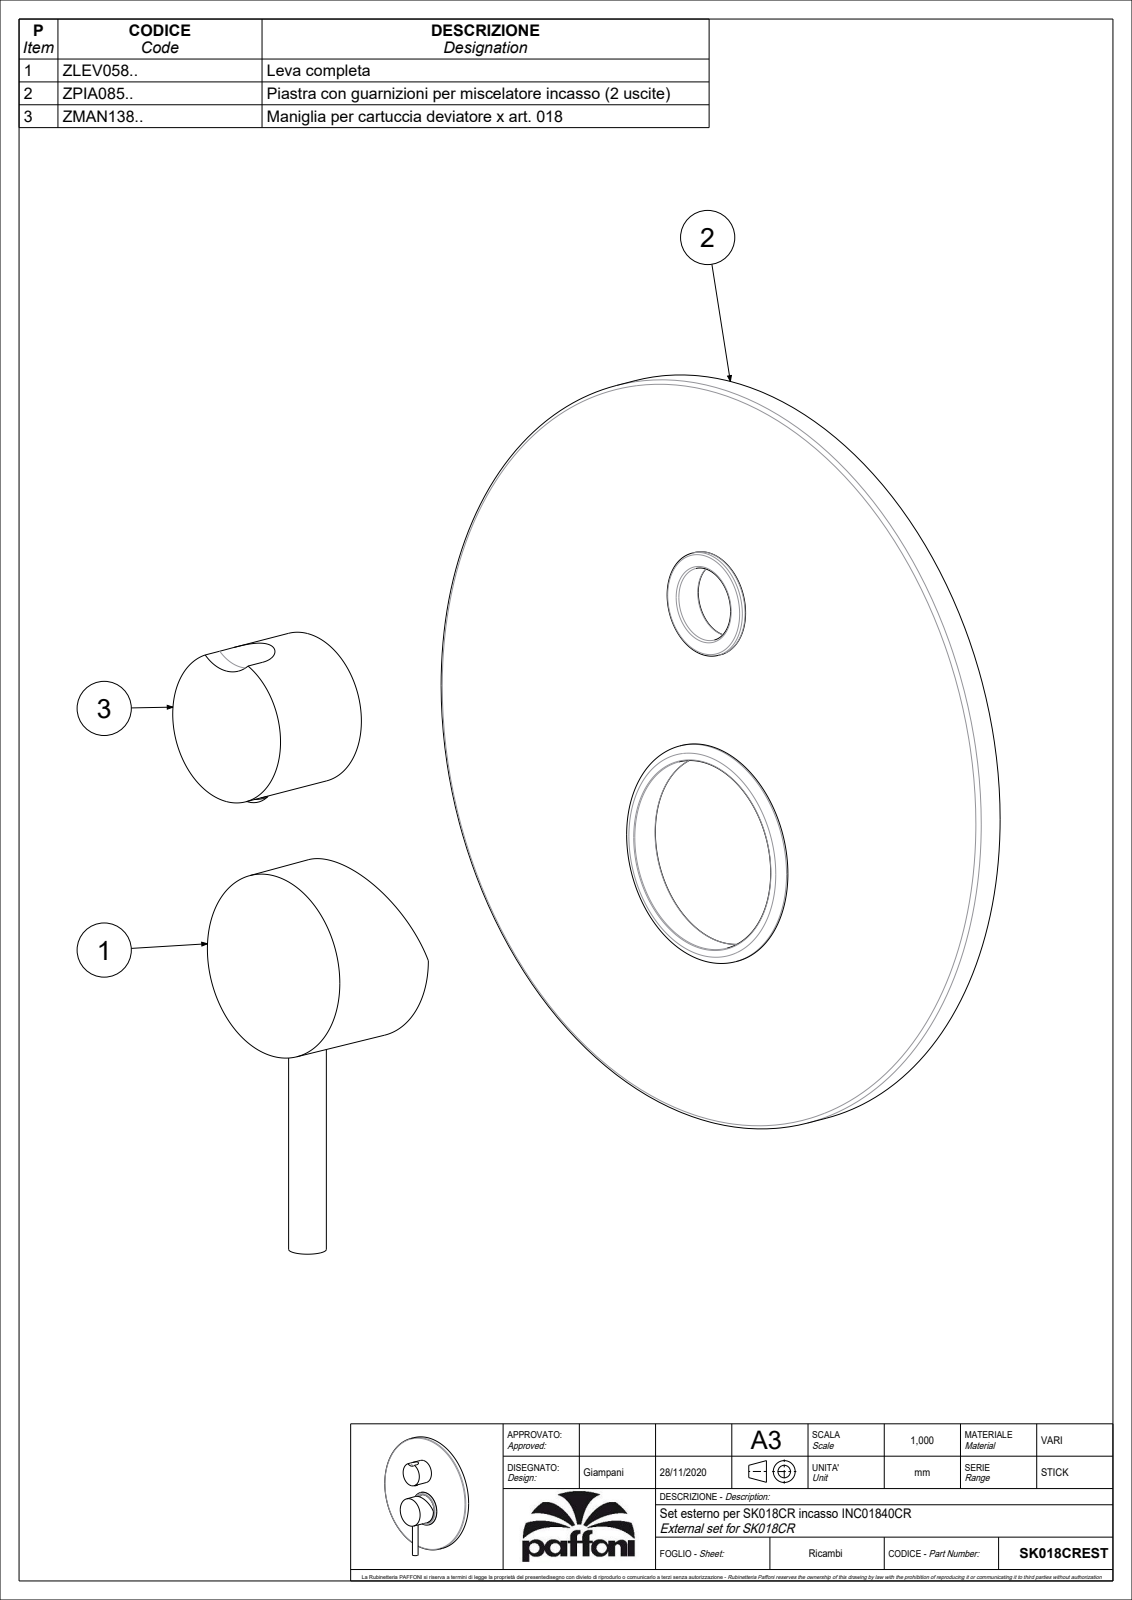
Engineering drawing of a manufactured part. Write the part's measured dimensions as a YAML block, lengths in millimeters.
part_name: "SK018CREST"
step_written_by: "CREO PARAMETRIC BY PTC INC, 2020044 (CONFIG_CONTROL_DESIGN)"
units: millimeters
bodies: {solids: 3, faces: 187, planar: 74, cylindrical: 58, other: 55}
overall_size: [206.1, 200, 46]
volume: 186318
surface_area: 104608
round_holes:
  - {diameter: 3, count: 1}
  - {diameter: 3.2, count: 1}
  - {diameter: 3.3, count: 1}
  - {diameter: 4.2, count: 1}
  - {diameter: 10, count: 1}
  - {diameter: 14.8, count: 1}
  - {diameter: 19.1, count: 1}
  - {diameter: 36, count: 1}
  - {diameter: 50.5, count: 1}
  - {diameter: 145, count: 1}
  - {diameter: 198, count: 1}
round_bosses_or_shafts:
  - {diameter: 200, count: 1}
  - {diameter: 195, count: 1}
  - {diameter: 58.5, count: 1}
  - {diameter: 54, count: 1}
  - {diameter: 40, count: 1}
  - {diameter: 25.1, count: 1}
  - {diameter: 24, count: 1}
  - {diameter: 23.5, count: 1}
partial_cylinders:
  - {radius: 6.5, count: 1}
  - {radius: 12.5, count: 1}
face_to_face_distances: [1, 8, 9, 35, 34, 43, 5, 18, 7, 19]
hole_center_spacings: [10, 26.75, 41.25, 51.25, 68, 78]
